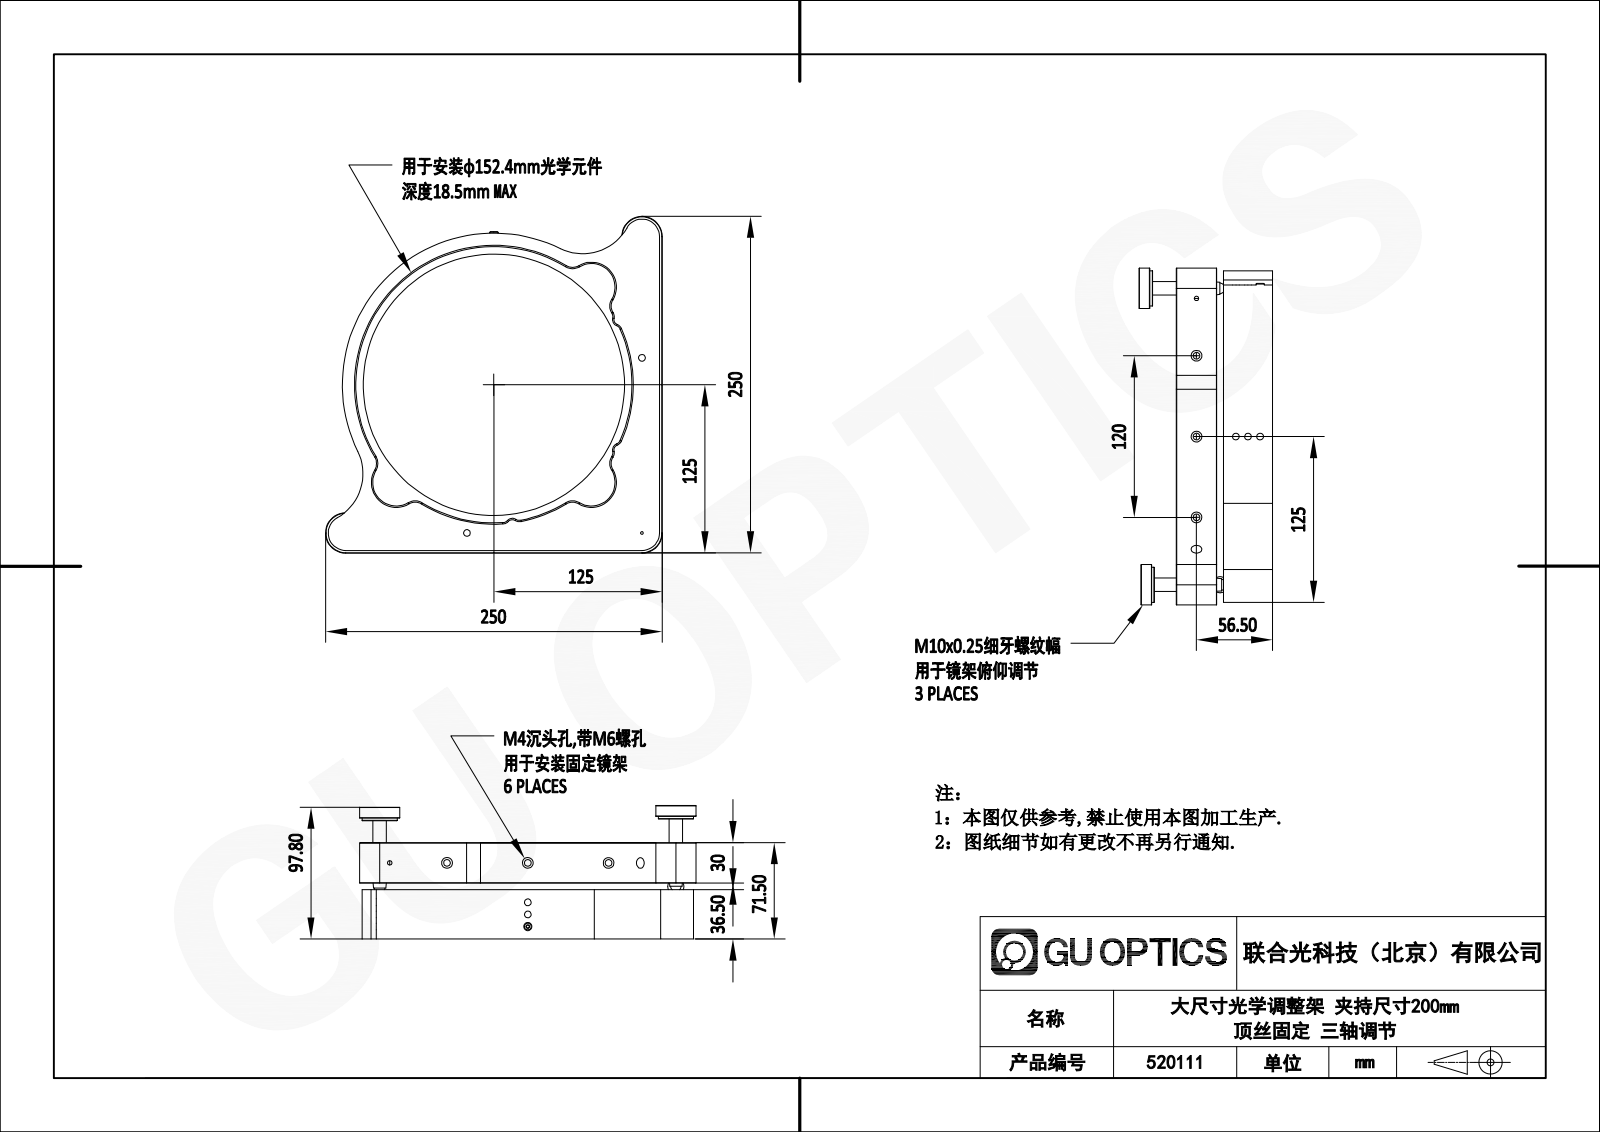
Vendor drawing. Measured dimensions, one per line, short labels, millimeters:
written by: SolidWorks 2021 (CONFIG_CONTROL_DESIGN)
unit: mm
bodies: 0 solids, 385 faces (99 planar, 192 cylindrical, 94 other)
size: 250 × 250 × 99.1
holes: 14× ⌀5, 9× ⌀3.3, 6× ⌀8, 6× ⌀9, 3× ⌀7, 3× ⌀15, 2× ⌀13, 1× ⌀2, 1× ⌀194
bosses: 3× ⌀30, 3× ⌀26, 3× ⌀20, 3× ⌀10, 1× ⌀6, 1× ⌀4.5
rounds: 12× R1.05, 9× R5, 6× R10, 4× R6, 3× R17.5, 2× R30, 2× R37.5, 1× R102.5
face distances: 30, 36.5, 2, 5, 41.5, 35, 71.5, 7, 37, 34.5
hole spacings: 60, 130, 9, 35, 66.75, 71.16, 76.37, 95
